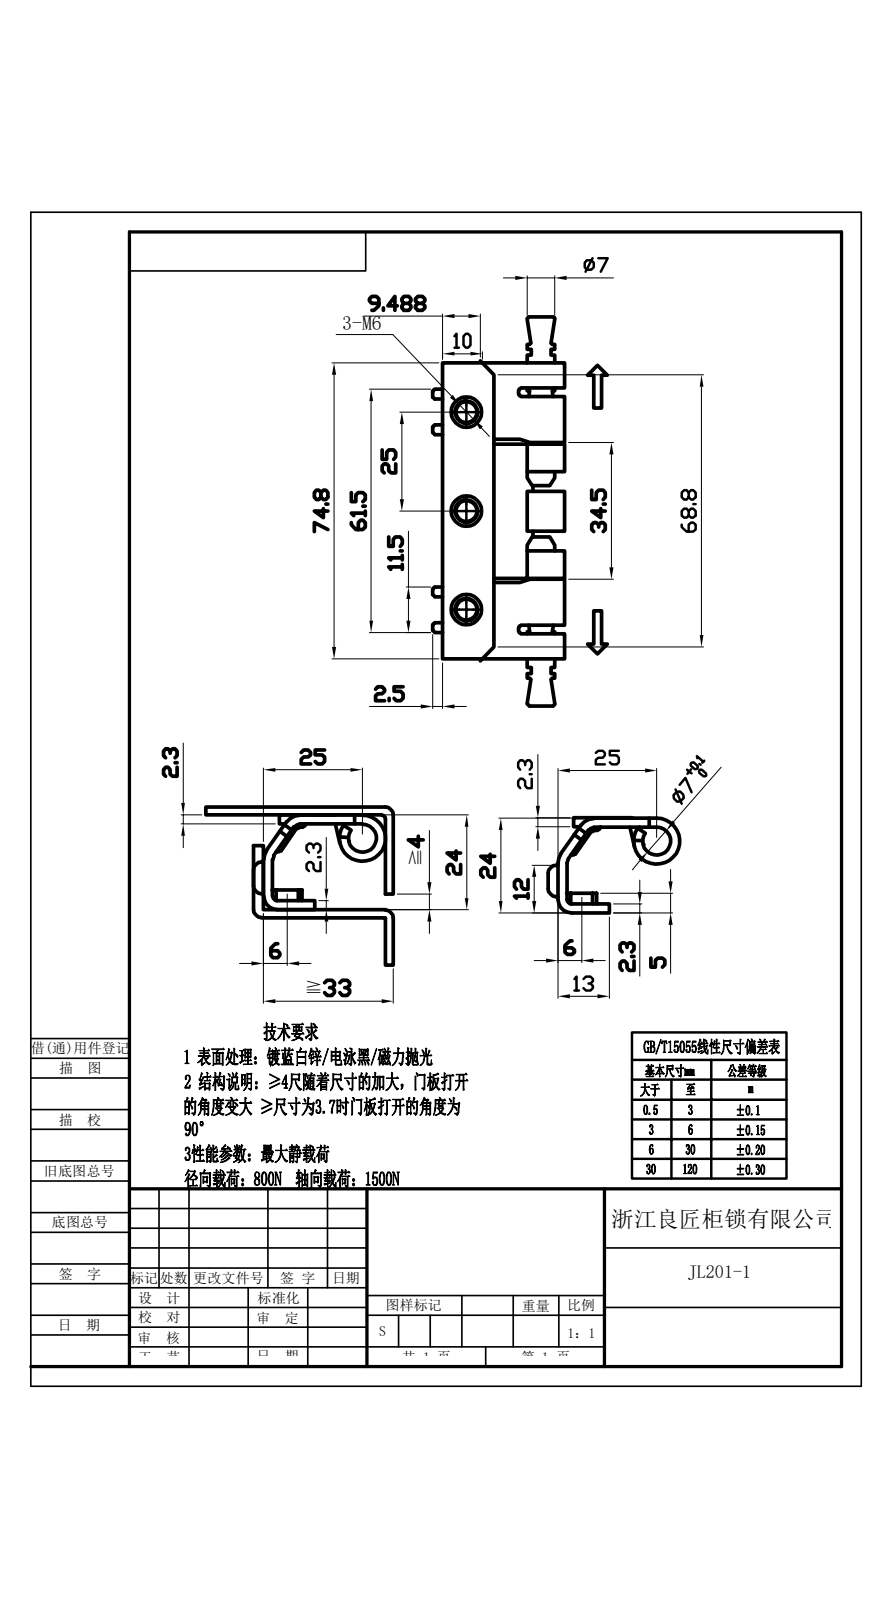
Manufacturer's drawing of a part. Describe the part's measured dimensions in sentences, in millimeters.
Its 3-D file was written by "Rhino 8.5 (CONFIG_CONTROL_DESIGN)". It is 4 solids with 281 faces: 60 planar, 126 cylindrical and 95 other. Overall it measures 98.2 by 30.85 by 24.1 millimeters. Its volume is 14 822 cubic millimeters and its surface area 14 388 square millimeters. Round holes: 3 of diameter 5.65, 2 of diameter 6.2, 1 of diameter 7.1. Round bosses or shafts: 1 of diameter 11.7, 1 of diameter 7.22, 1 of diameter 7, 1 of diameter 5. Partial cylindrical surfaces (rounded edges, fillets, slot ends): 21 of radius 0.5, 9 of radius 1, 8 of radius 0.9, 2 of radius 1.2, 2 of radius 1.5, 2 of radius 3.5, 1 of radius 2, 1 of radius 3. The main face-to-face distances are 2.3, 21.7, 21.8, 19.4, 2.29, 24, 2.2, 24.1, 2.4, 19.5. The hole center spacings are 8.14, 18.36, 25, 32.33, 14.16, 50.
